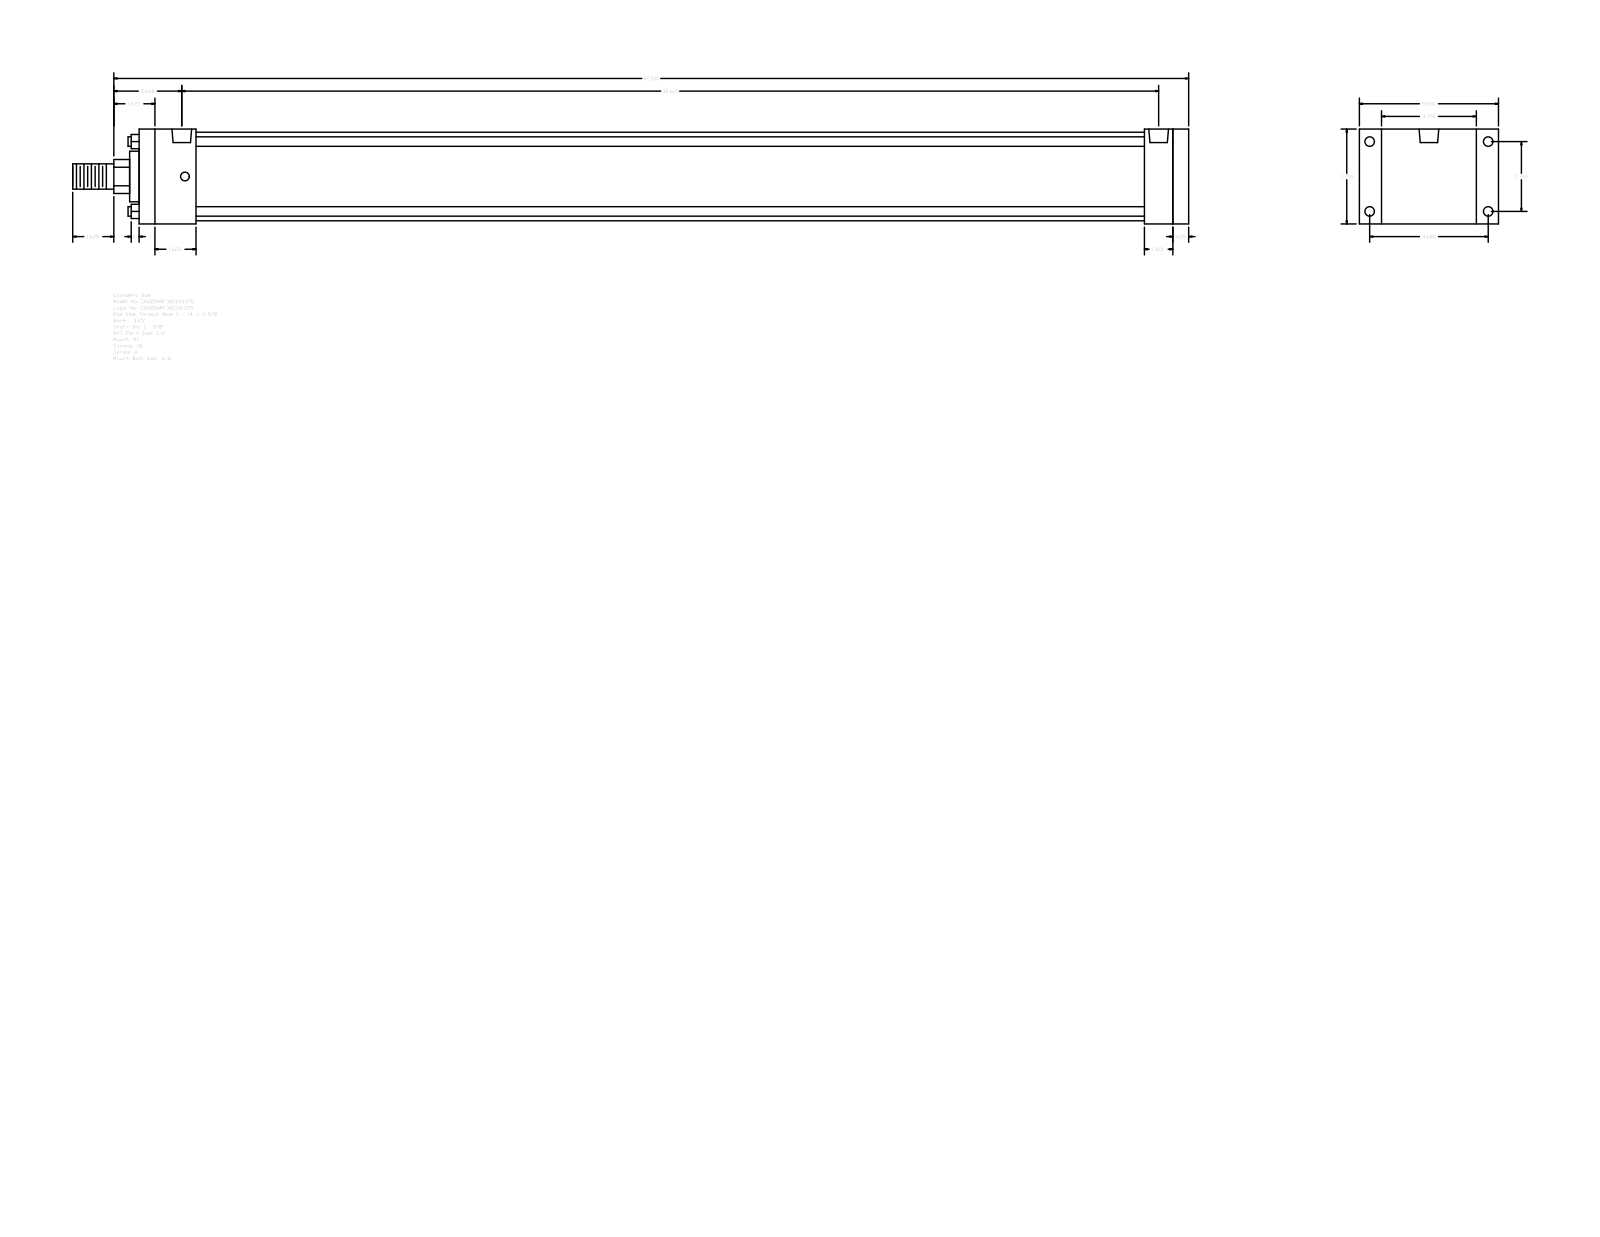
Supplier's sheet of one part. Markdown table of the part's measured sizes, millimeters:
| quantity | value |
| --- | --- |
| part name | A_RF__0325_1.375 |
| STEP written by | GSSL Pune (CONFIG_CONTROL_DESIGN) |
| units | millimeters |
| bodies | 0 solids, 92 faces (64 planar, 28 cylindrical, 0 other) |
| overall size | 1120.78 × 139.7 × 95.25 |
| round holes (diameter × count) | 8.73 × 4, 9.53 × 4, 19.77 × 2 |
| round bosses / shafts (diameter × count) | 9.53 × 4, 88.9 × 1, 50.8 × 1, 34.92 × 1, 25.4 × 1 |
| partial cylindrical surfaces (radius × count) | 17.06 × 1 |
| main face-to-face distances | 95.24, 1054.1, 15.88, 1038.22, 57.15, 22.23, 117.47, 1009.65, 28.57, 44.45 |
| hole center spacings | 3.18, 70.1, 119.06, 138.16, 974.72, 977.9, 981.08 |
